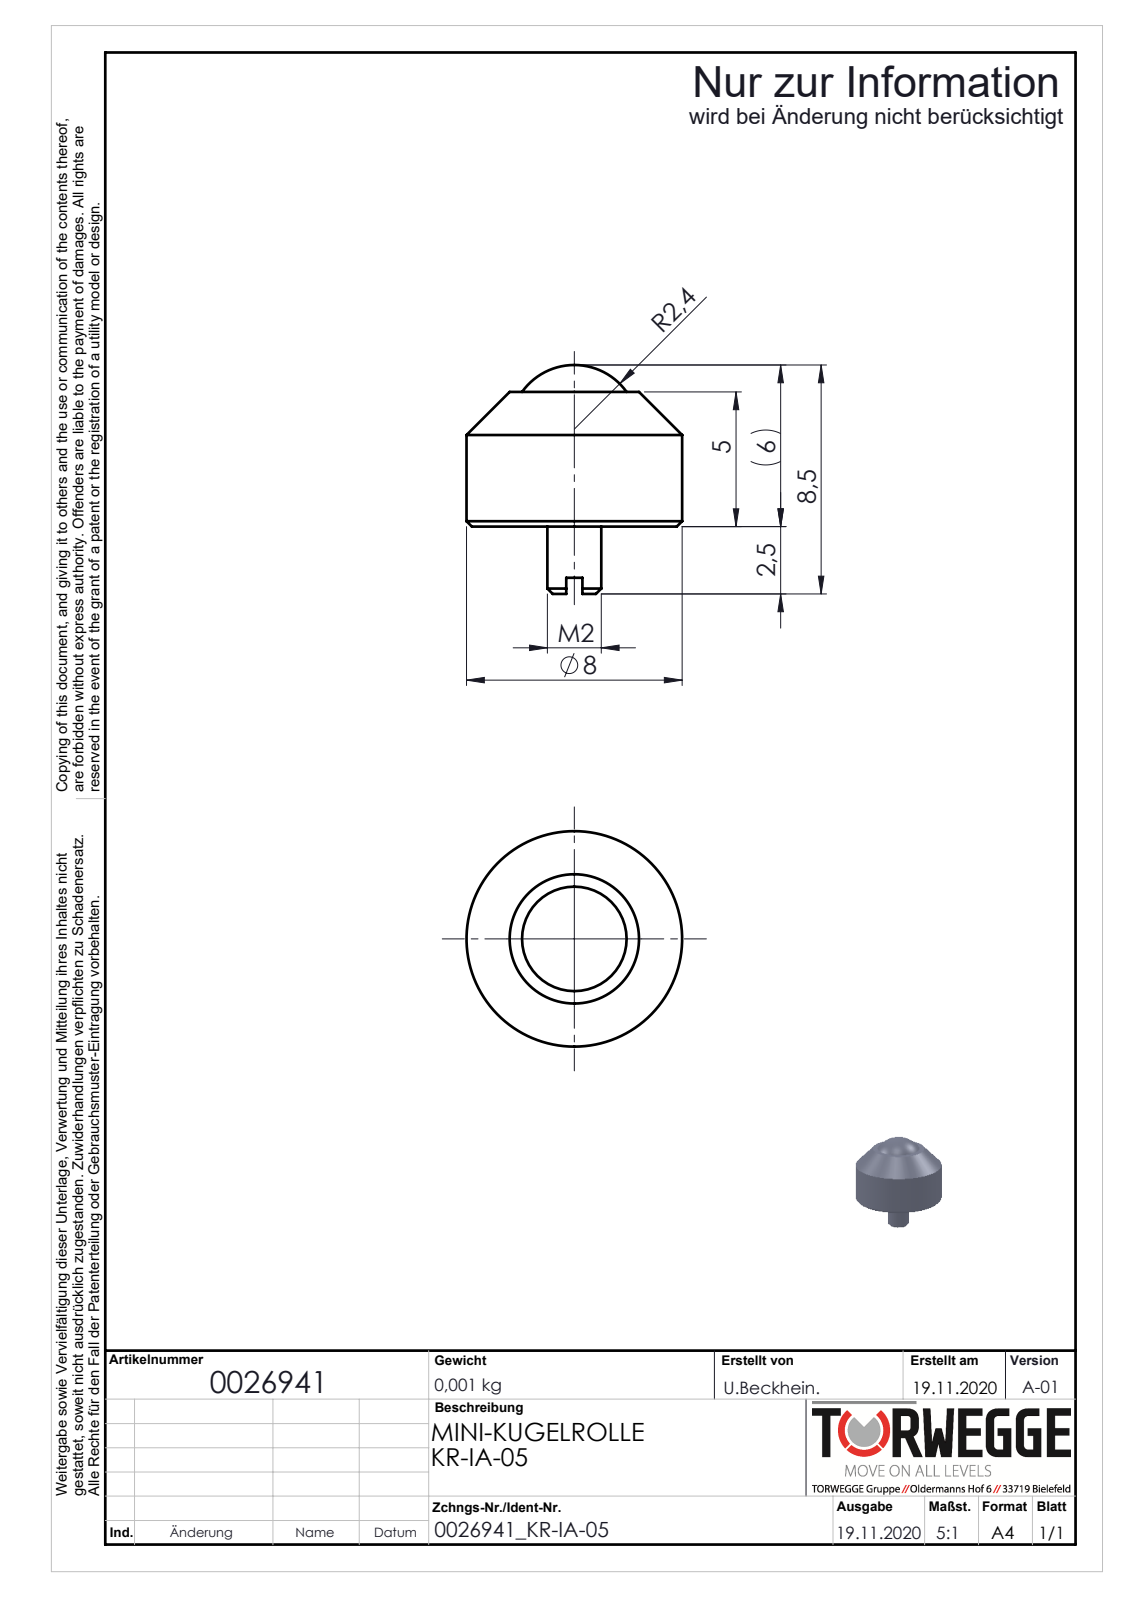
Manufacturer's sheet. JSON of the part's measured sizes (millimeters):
{"part_name": "0026941", "step_written_by": "SolidWorks 2018 (AUTOMOTIVE_DESIGN)", "units": "millimeters", "bodies": {"solids": 1, "faces": 20, "planar": 7, "cylindrical": 4, "other": 9}, "overall_size": [8.5, 8, 8], "volume_mm3": 236, "surface_area_mm2": 216, "round_bosses_or_shafts": [[8, 1], [2, 1]], "face_to_face_distances": [5, 0.6, 1.9, 6.9, 2.5, 7.5]}
